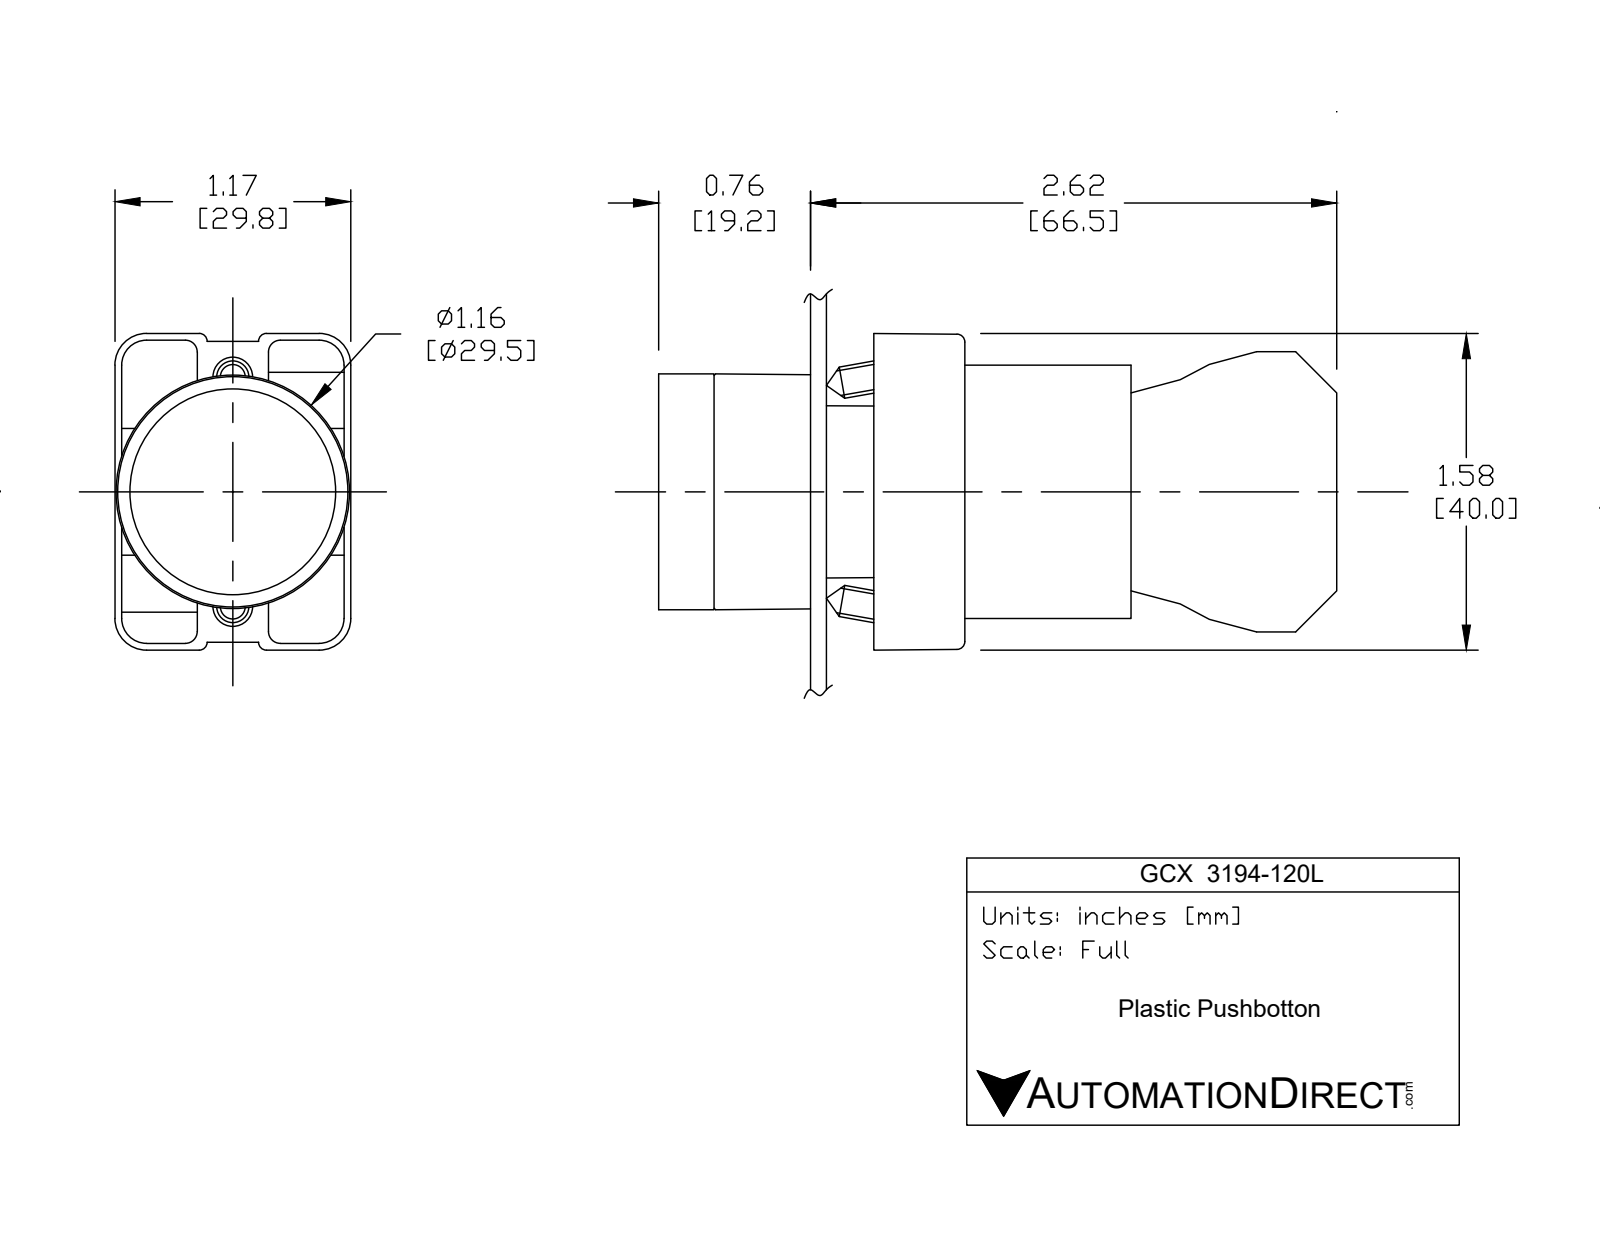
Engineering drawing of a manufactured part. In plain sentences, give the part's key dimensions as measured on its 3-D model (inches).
The part is named "CONTACT BLOCK; GCX3194-120L; ECX3029-2; GCX3194L OPERATOR (+1 more)". Its 3-D file was written by "SolidWorks 2016 (AUTOMOTIVE_DESIGN)". It is 8 solids with 431 faces: 252 planar, 148 cylindrical and 31 other. Overall it measures 3.319 by 1.581 by 1.177 inches. Its volume is 2.794 cubic inches and its surface area 38.77 square inches. Round holes: 2 of diameter 0.079, 2 of diameter 0.124, 2 of diameter 0.13, 1 of diameter 0.087, 1 of diameter 0.197, 1 of diameter 0.469, 1 of diameter 0.878, 1 of diameter 0.888, 1 of diameter 1.024. Round bosses or shafts: 4 of diameter 0.157, 1 of diameter 1.175, 1 of diameter 1.004, 1 of diameter 0.945, 1 of diameter 0.856, 1 of diameter 0.78, 1 of diameter 0.504. Partial cylindrical surfaces (rounded edges, fillets, slot ends): 24 of radius 0.059, 12 of radius 0.041, 12 of radius 0.124, 12 of radius 0.157, 8 of radius 0.039, 2 of radius 0.128, 1 of radius 0.02, 1 of radius 0.063. The main face-to-face distances are 0.827, 0.579, 2.02, 1.193, 1.171, 0.276, 2.295, 1.469, 0.031, 0.033. The hole center spacings are 0.236, 0.544, 0.472, 0.49.
